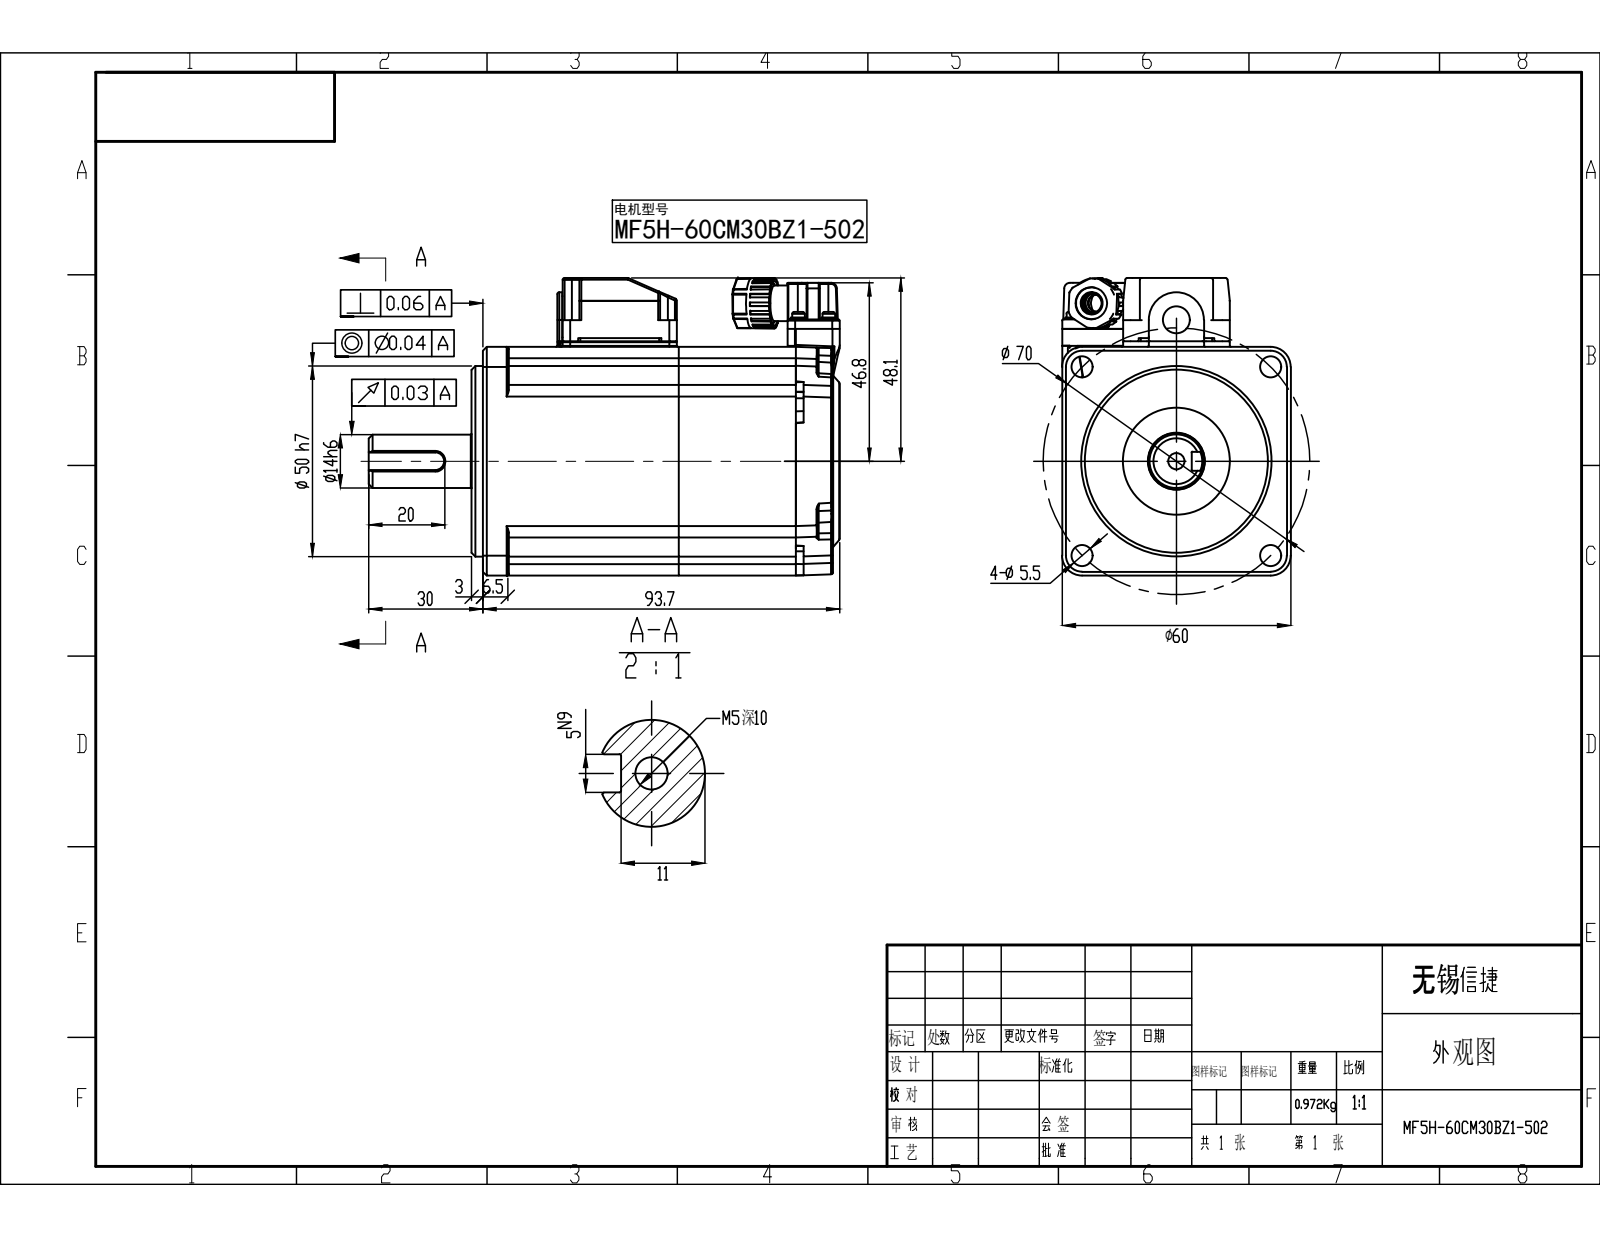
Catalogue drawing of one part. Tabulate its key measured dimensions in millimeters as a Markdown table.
| quantity | value |
| --- | --- |
| part name | MF5H-60CM30BZ1-502 |
| STEP written by | SolidWorks 2022 (CONFIG_CONTROL_DESIGN) |
| units | millimeters |
| bodies | 0 solids, 801 faces (281 planar, 280 cylindrical, 240 other) |
| overall size | 123.65 × 78.19 × 60.18 |
| round holes (diameter × count) | 5.5 × 5, 2.3 × 4, 3.5 × 3, 4.2 × 1, 5 × 1, 7.1 × 1, 11.7 × 1, 15 × 1 |
| round bosses / shafts (diameter × count) | 3.9 × 4, 3.3 × 4, 50 × 1, 28 × 1, 14 × 1, 9.4 × 1 |
| partial cylindrical surfaces (radius × count) | 0.5 × 66, 0.3 × 52, 2 × 20, 3 × 17, 0.2 × 15, 5 × 7, 1.5 × 6, 2.25 × 4 |
| main face-to-face distances | 60, 11.5, 96.65, 85.15, 10, 3, 93.65, 82.15, 50, 1.8 |
| hole center spacings | 35, 49.5, 8.55, 31.64, 41.31, 52.4, 66.18, 23.6 |
